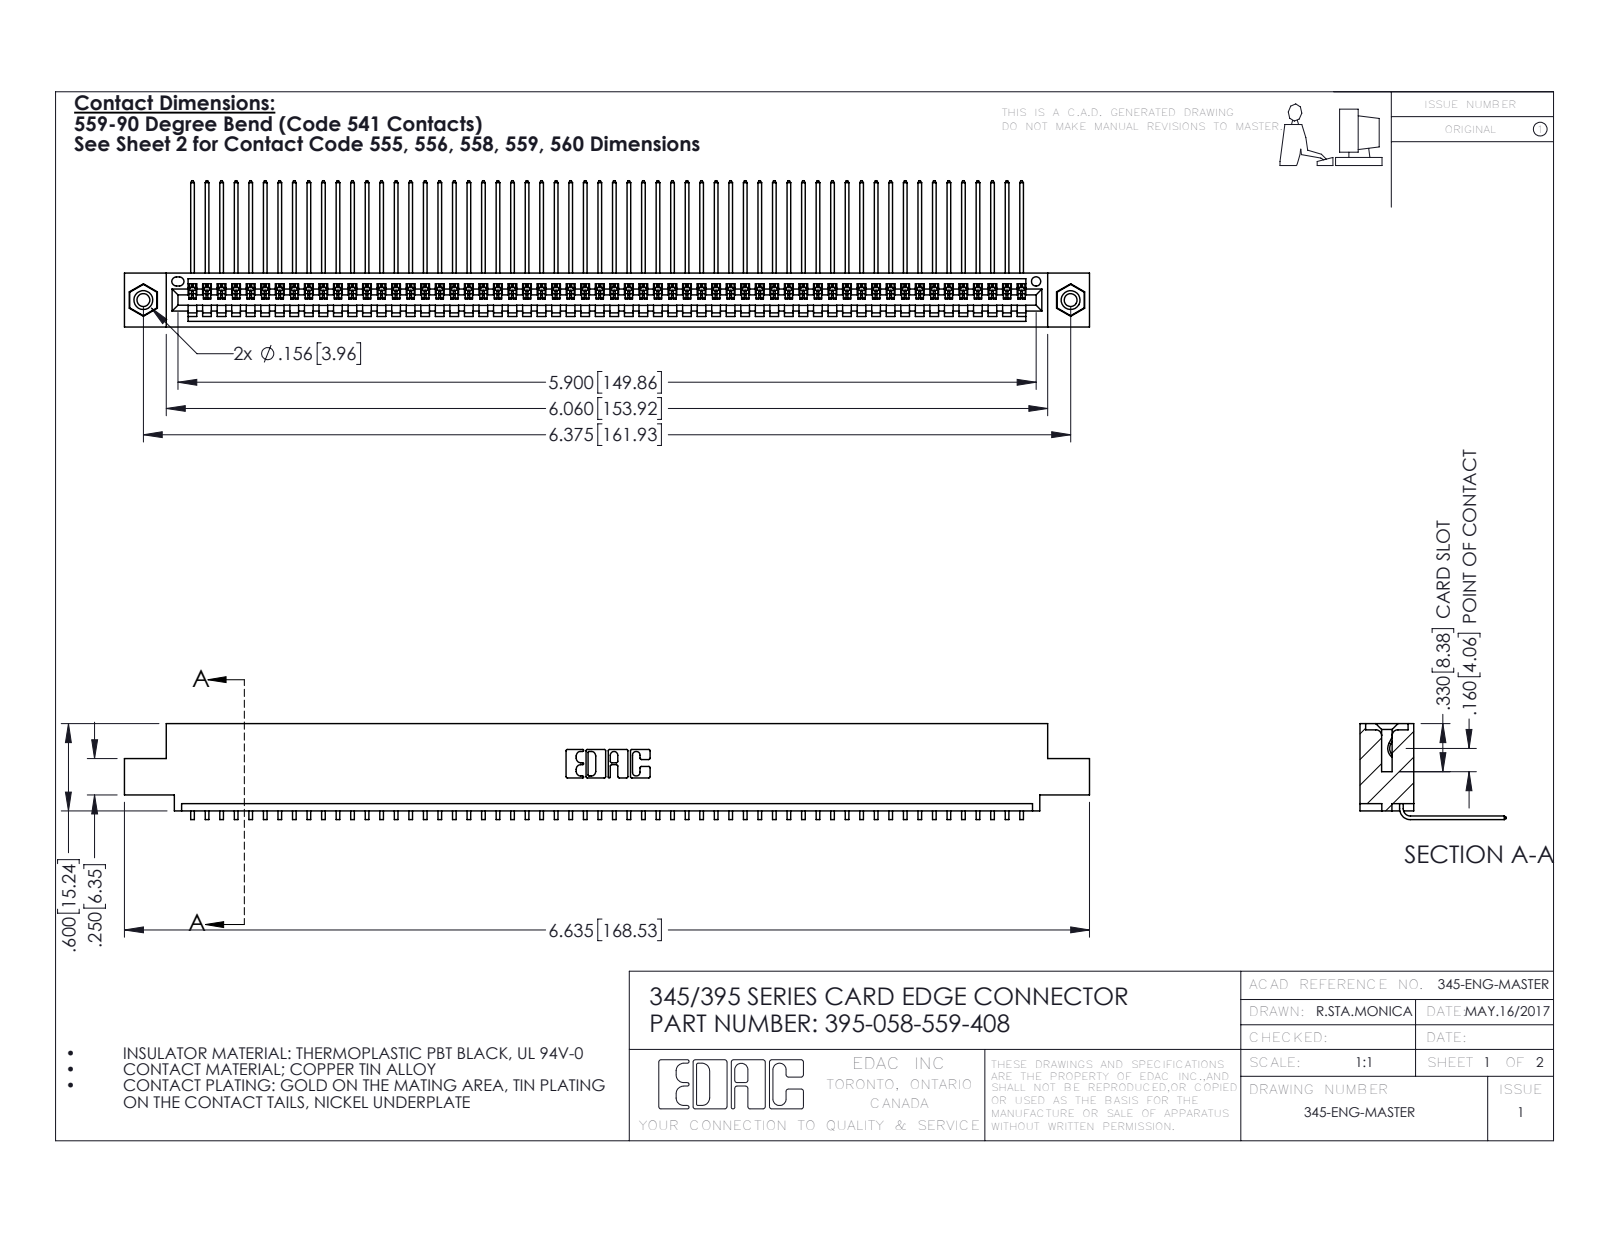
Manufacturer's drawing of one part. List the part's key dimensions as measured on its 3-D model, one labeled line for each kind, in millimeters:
Part name (STEP PRODUCT): 395-058-559-408; 345-250-001_345-250-003-102; 345-292-001_558 559 Tail - 1; 345 Part_0.110 Offset - 0.156 Dia-TI
STEP written by: SolidWorks 2016 (CONFIG_CONTROL_DESIGN)
Units: millimetres
Bodies: 61 solids, 3670 faces (2552 planar, 1102 cylindrical, 16 other)
Overall size (bounding box): 168.5 × 25.5 × 16.7
Volume: 16 300 mm³ · Surface area: 23 050 mm²
Round holes (diameter × count): ⌀2.3 ×2, ⌀3.2 ×2, ⌀4 ×2, ⌀1.6 ×1
Round bosses / shafts (diameter × count): ⌀3.9 ×2
Partial cylindrical surfaces — rounded edges, fillets, slot ends (radius × count): R0.2 ×116, R0.3 ×22, R0.2 ×6, R0.8 ×6, R0.7 ×3, R0.8 ×2, R1 ×2, R0.4 ×1
Main face-to-face distances: 1.8, 7.6, 9.4, 5.1, 2.5, 6.9, 0.6, 5.7, 3.8, 1.8
Hole centre spacings: 6.9, 155.9, 161.9
